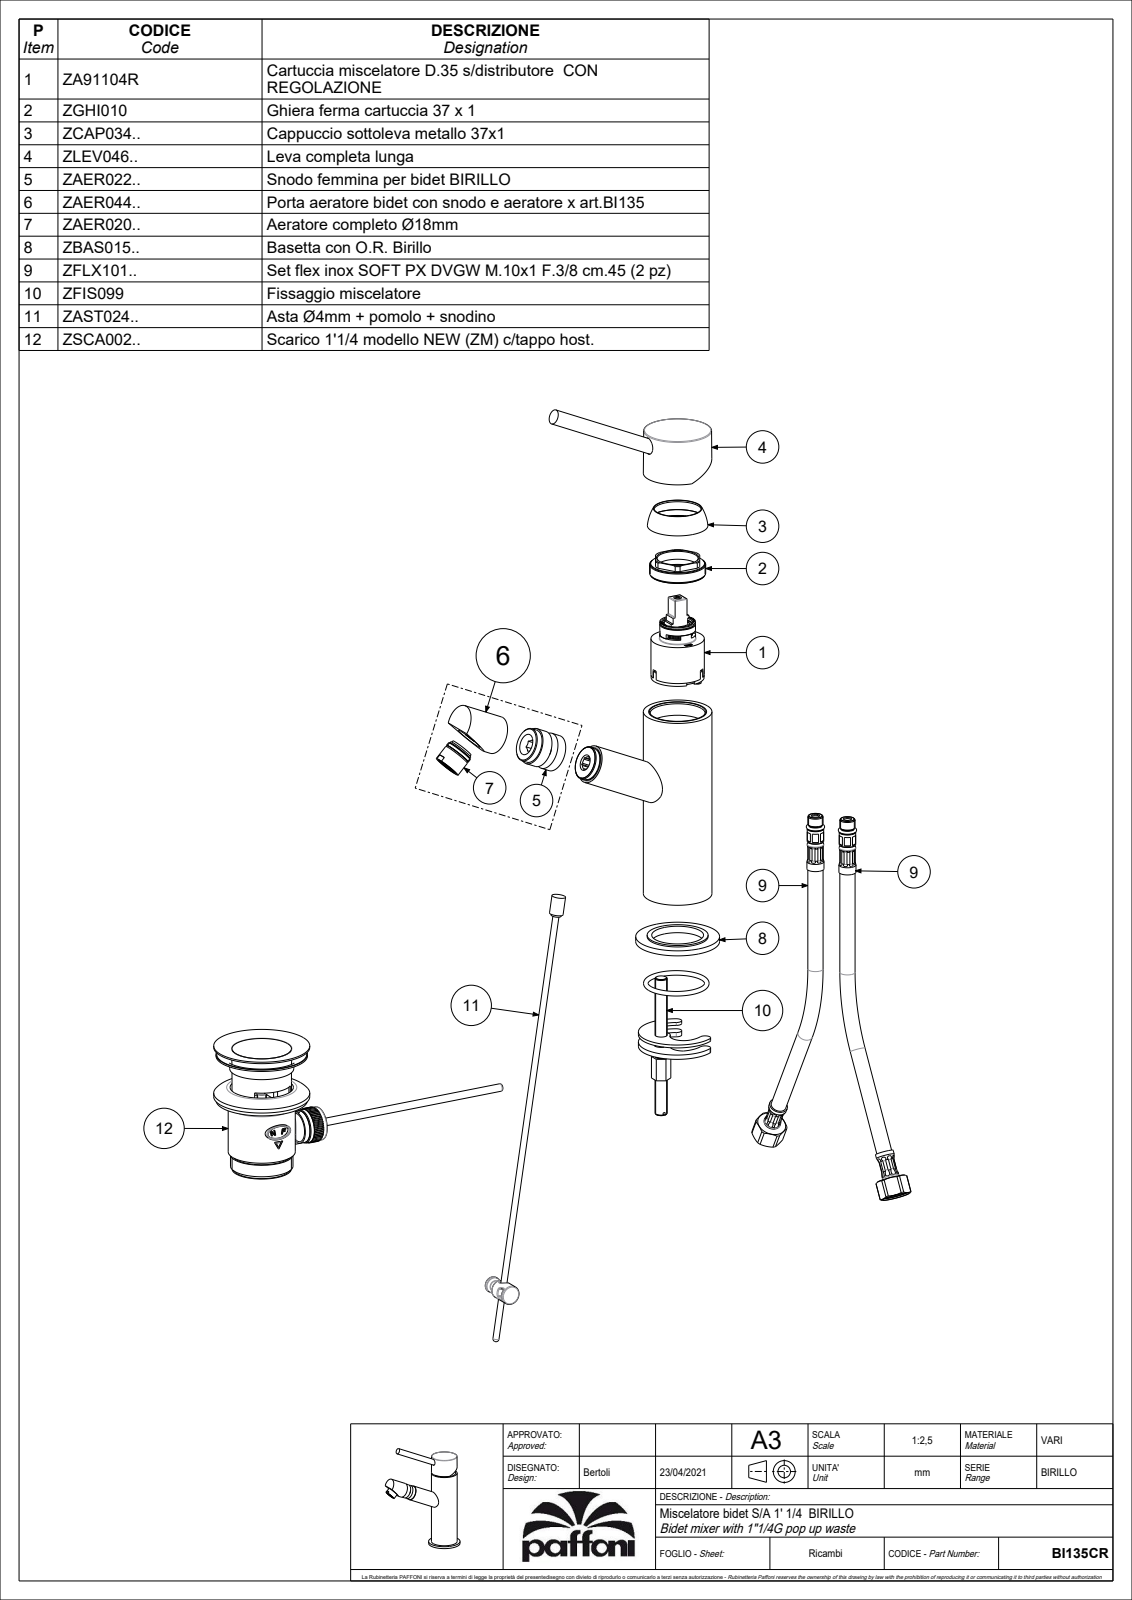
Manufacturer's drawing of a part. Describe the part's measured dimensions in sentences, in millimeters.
The part is named "BI135CR". Its 3-D file was written by "CREO PARAMETRIC BY PTC INC, 2020044 (CONFIG_CONTROL_DESIGN)". It is 3 solids with 1081 faces: 596 planar, 264 cylindrical and 221 other. Overall it measures 192.84 by 150.49 by 55 millimeters. Its volume is 232 913 cubic millimeters and its surface area 74 590 square millimeters. Round holes: 3 of diameter 11, 2 of diameter 4, 2 of diameter 4.5, 2 of diameter 5, 2 of diameter 6.5, 2 of diameter 9, 1 of diameter 3.3, 1 of diameter 7.25, 1 of diameter 10, 1 of diameter 15.5, 1 of diameter 18.2, 1 of diameter 19.5. Round bosses or shafts: 2 of diameter 25, 1 of diameter 55, 1 of diameter 45, 1 of diameter 40, 1 of diameter 37, 1 of diameter 35, 1 of diameter 34.8, 1 of diameter 32.2. Partial cylindrical surfaces (rounded edges, fillets, slot ends): 51 of radius 0.5, 11 of radius 0.15, 4 of radius 0.3, 2 of radius 1, 1 of radius 3, 1 of radius 5, 1 of radius 7, 1 of radius 9.3. The main face-to-face distances are 132.1, 26.5, 3.5, 4.5, 5.5, 121.5, 104.3, 100.8, 23, 77.8. The hole center spacings are 3.54, 8.06, 8.75, 10.97, 14.01, 15.89, 12.5, 15.
